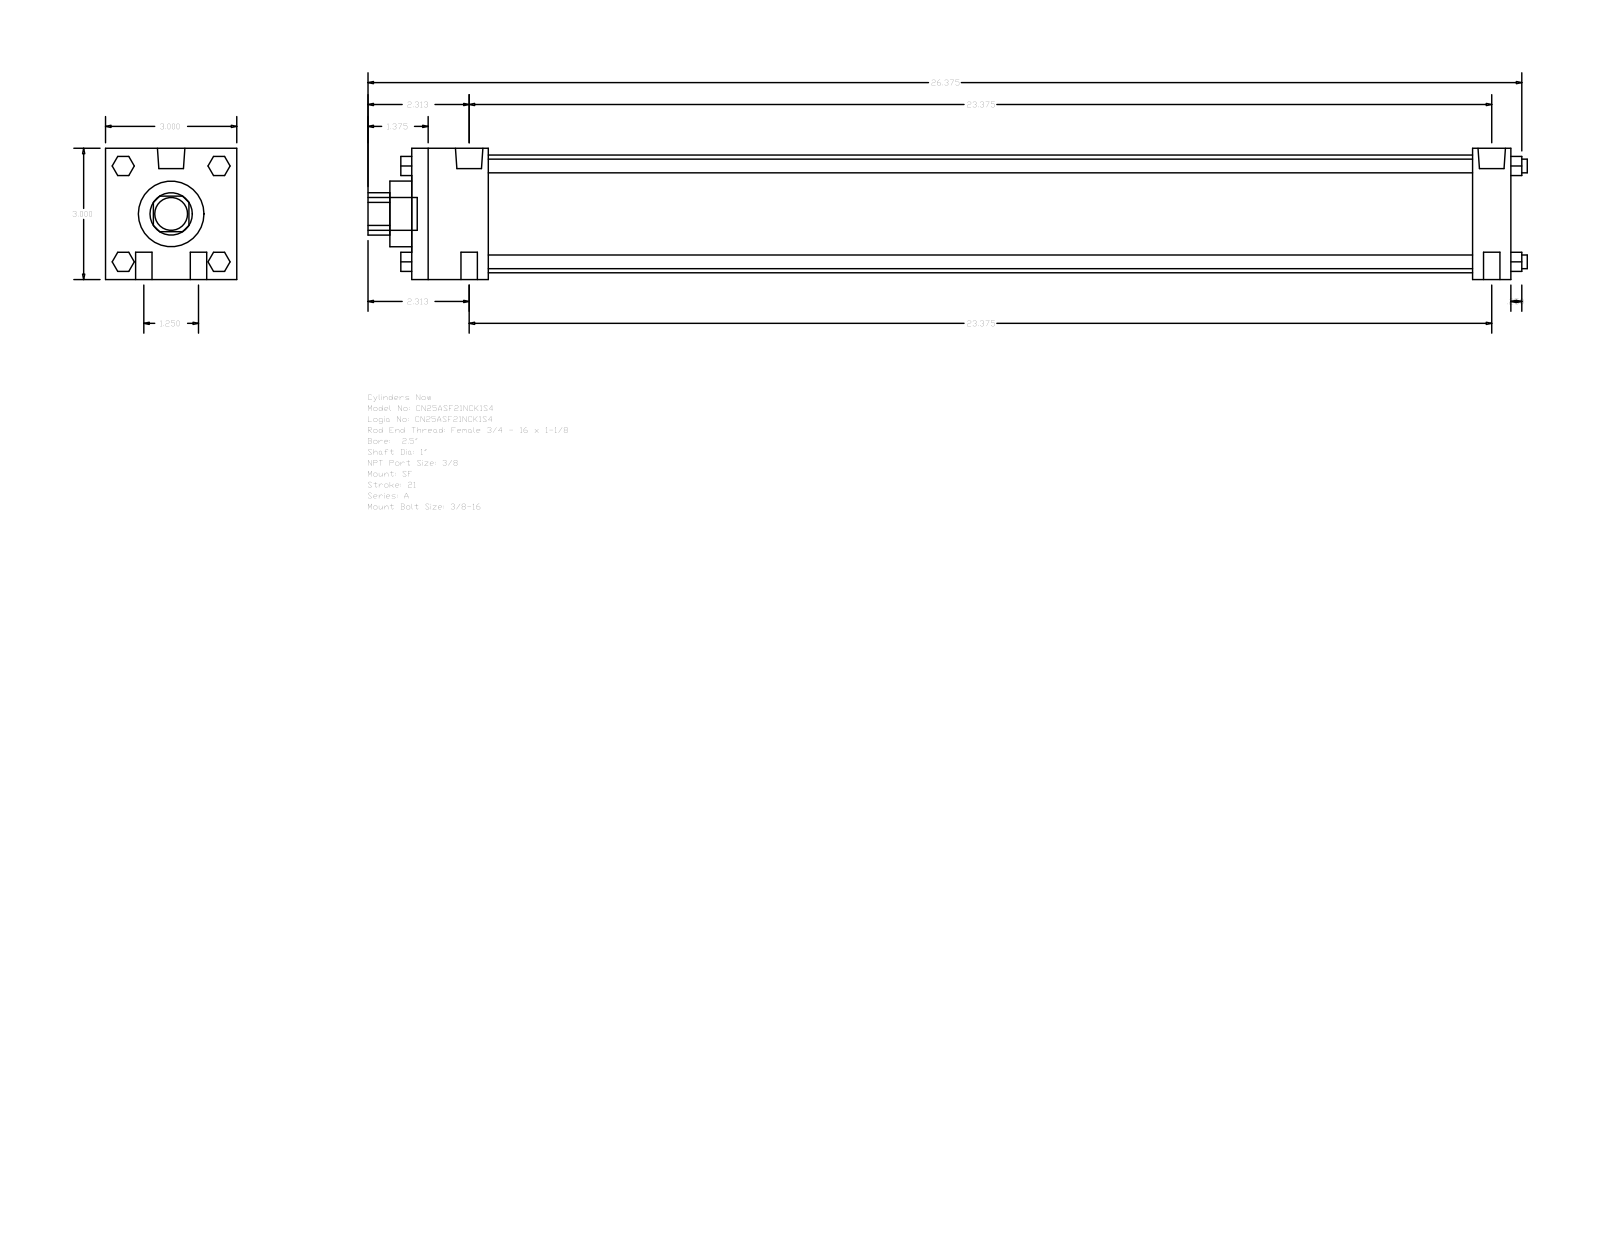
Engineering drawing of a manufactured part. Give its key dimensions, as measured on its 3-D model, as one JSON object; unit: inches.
{"part_name": "A_SF__0250_1", "step_written_by": "GSSL Pune (CONFIG_CONTROL_DESIGN)", "units": "inches", "bodies": {"solids": 0, "faces": 124, "planar": 94, "cylindrical": 30, "other": 0}, "overall_size": [26.5, 3, 3], "round_holes": [[1, 1], [1.5, 1], [2.69, 1]], "round_bosses_or_shafts": [[0.375, 4], [0.313, 4], [0.627, 2], [0.219, 2], [0.75, 1]], "partial_cylinders_radius": [[0.484, 1]], "face_to_face_distances": [3, 25.125, 24.25, 0.875, 1.75, 22.5, 23.375, 0.5, 0.437, 2.25]}
